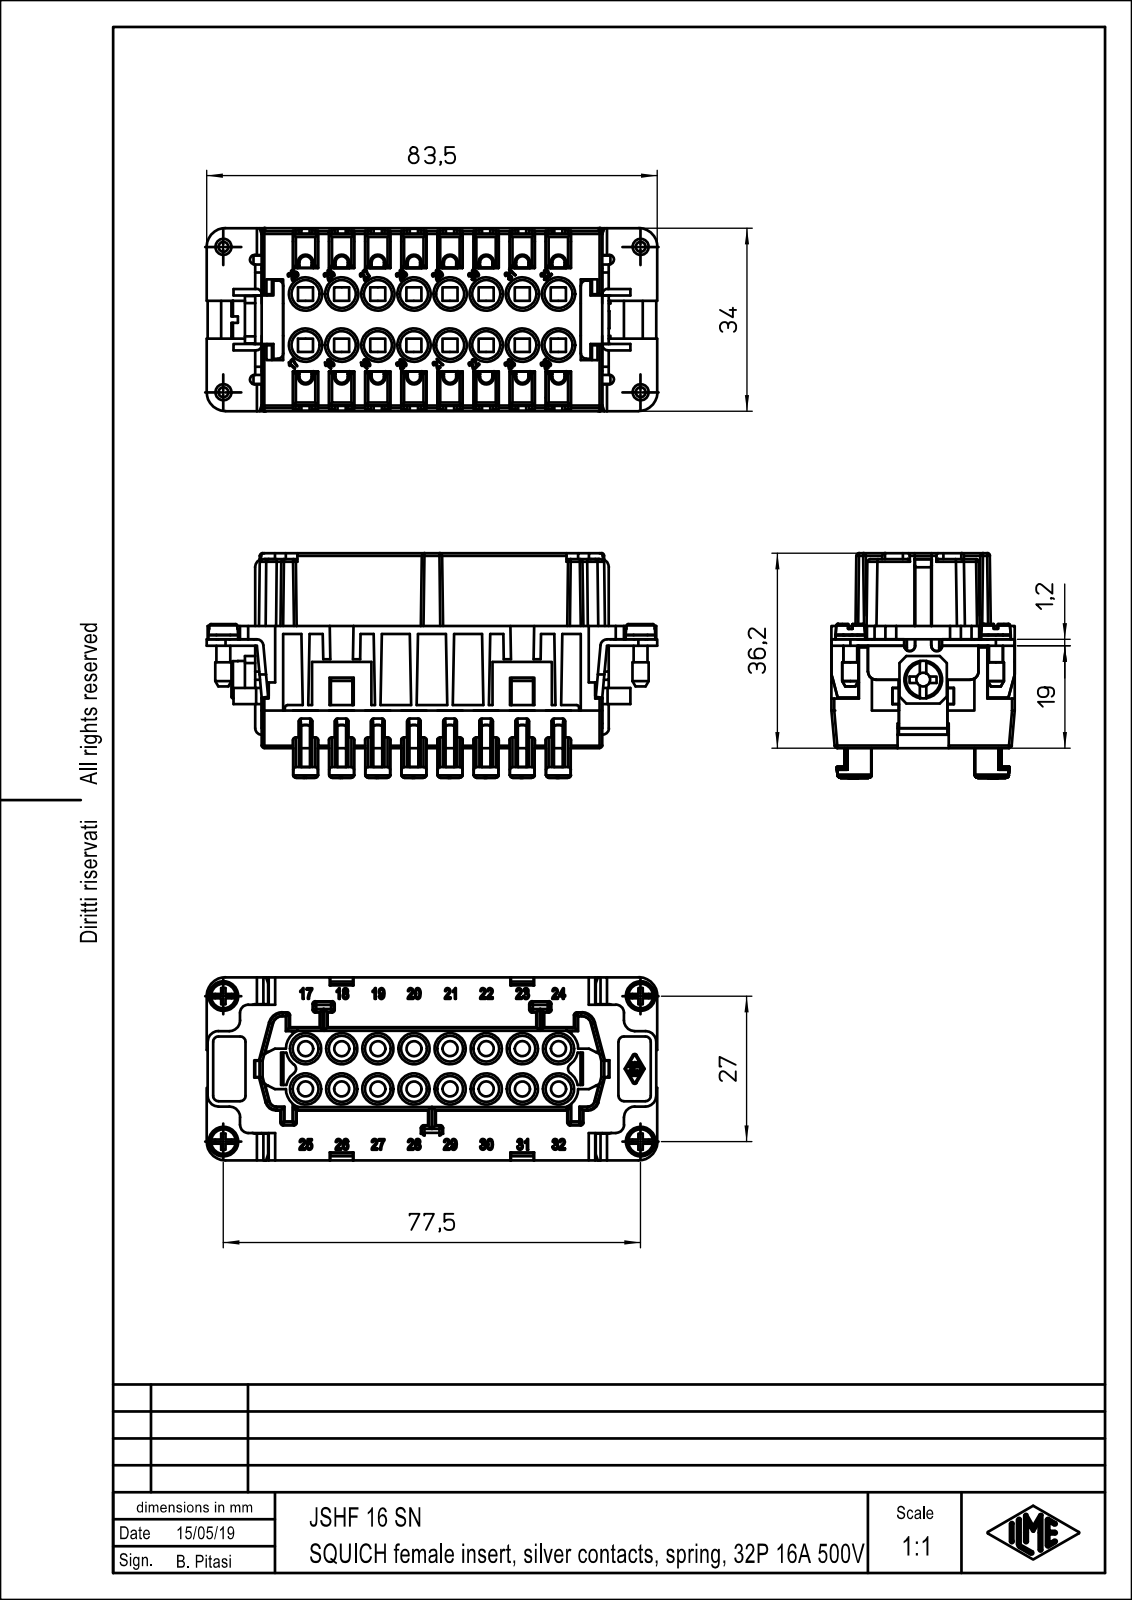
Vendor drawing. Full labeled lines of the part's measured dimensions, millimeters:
Part name (STEP PRODUCT): JSHF_16_SN
STEP written by: Creo Elements/Direct Modeling 20.1B 02-Apr-2019 (C) Parametric Technology GmbH (AUTOMOTIVE_DESIGN)
Units: millimetres
Bodies: 1 solid, 2084 faces (1305 planar, 620 cylindrical, 159 other)
Overall size (bounding box): 83.6 × 41.7 × 34
Volume: 55 608 mm³ · Surface area: 29 523 mm²
Round holes (diameter × count): ⌀2.8 ×20, ⌀5.2 ×16, ⌀5.8 ×16, ⌀2.58 ×1, ⌀4.2 ×1
Round bosses / shafts (diameter × count): ⌀5.5 ×4, ⌀3 ×4, ⌀2.6 ×4, ⌀7 ×1, ⌀6 ×1, ⌀4 ×1
Partial cylindrical surfaces — rounded edges, fillets, slot ends (radius × count): R0.5 ×171, R0.3 ×40, R1 ×22, R1.15 ×16, R1.5 ×10, R2 ×10, R1.2 ×6, R0.88 ×4
Main face-to-face distances: 1.5, 6.7, 1.2, 13.4, 12.5, 20.1, 32.5, 2.5, 22.7, 19
Hole centre spacings: 6.7, 6.77, 10.82, 13.4, 13.44, 15.87, 20.1, 20.12
